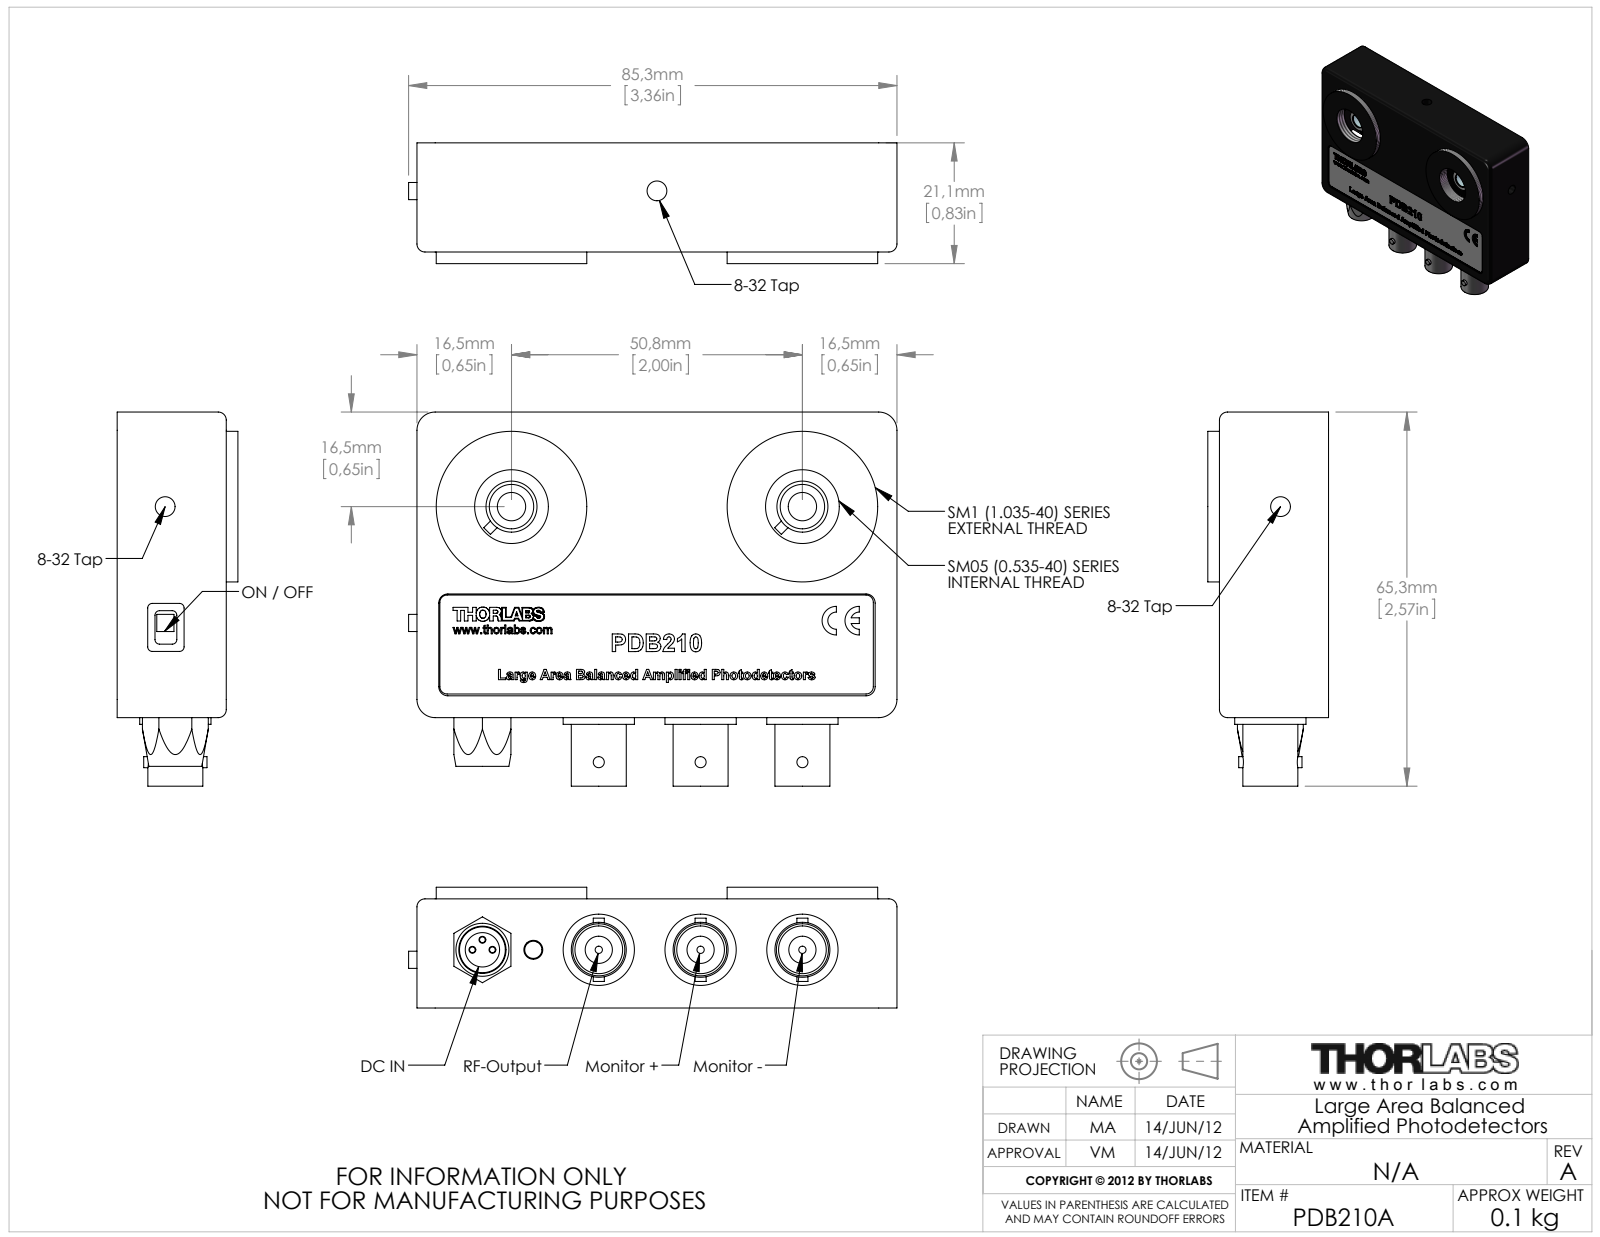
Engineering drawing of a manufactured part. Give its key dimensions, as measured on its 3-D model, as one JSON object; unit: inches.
{"part_name": "Schalter-01_Off; PDB210A-Schild-01_Metric; PDB2xx_web; M0092-0431-0A-(8-32)-Gehäuse ohne Laserbeschriftung_Etching (+6 more)", "step_written_by": "SolidWorks 2008 (CONFIG_CONTROL_DESIGN)", "units": "inches", "bodies": {"solids": 15, "faces": 2325, "planar": 1343, "cylindrical": 305, "other": 677}, "overall_size": [3.357, 2.571, 0.83], "volume_in3": 2.056, "surface_area_in2": 59.3, "round_holes": [[0.063, 7], [0.094, 4], [0.098, 4], [0.039, 3], [0.05, 3], [0.052, 3], [0.328, 3], [0.438, 3], [0.136, 2], [0.295, 2], [0.413, 2], [0.507, 2]], "round_bosses_or_shafts": [[0.02, 6], [0.118, 5], [0.044, 4], [0.49, 3], [0.43, 3], [0.378, 3], [0.37, 3], [0.323, 3]], "partial_cylinders_radius": [[0.125, 31], [0.13, 14], [0.031, 8], [0.095, 8], [0.05, 4], [0.055, 4], [0.11, 4], [0.024, 3]], "face_to_face_distances": [0.063, 0.1, 0.05, 0.68, 0.617, 0.73, 0.667, 0.02, 0.07, 0.75], "hole_center_spacings": [2.004, 0.069, 2, 0.097, 0.125, 0.125, 0.25, 0.525]}
